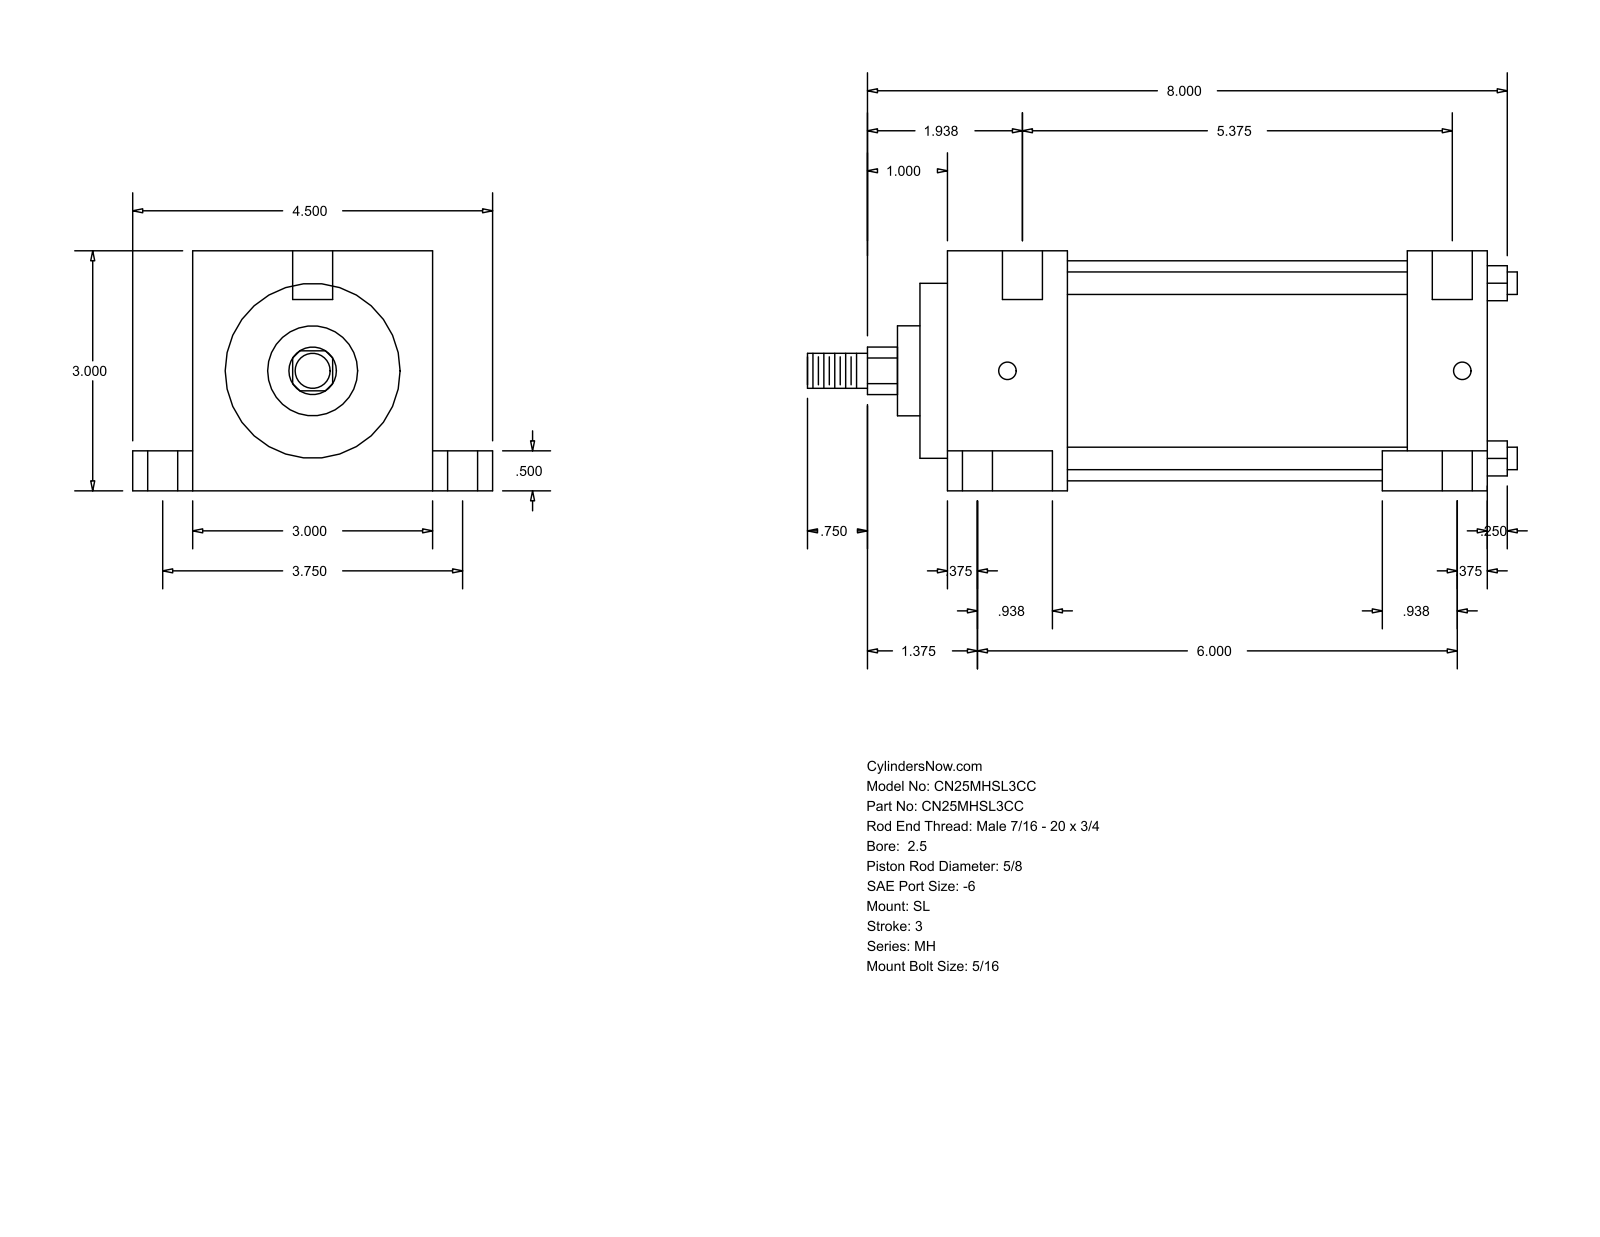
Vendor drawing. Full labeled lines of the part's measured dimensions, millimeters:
Part name (STEP PRODUCT): MH_SL__0250_0.625
STEP written by: GSSL Pune (CONFIG_CONTROL_DESIGN)
Units: millimetres
Bodies: 0 solids, 86 faces (61 planar, 25 cylindrical, 0 other)
Overall size (bounding box): 225.43 × 114.3 × 76.2
Round holes (diameter × count): ⌀5.56 ×2, ⌀9.53 ×2, ⌀15.88 ×2, ⌀12.7 ×1
Round bosses / shafts (diameter × count): ⌀7.14 ×4, ⌀69.85 ×1, ⌀55.55 ×1, ⌀28.57 ×1, ⌀15.88 ×1, ⌀11.11 ×1
Partial cylindrical surfaces — rounded edges, fillets, slot ends (radius × count): R7.54 ×1
Main face-to-face distances: 76.2, 25.4, 154.78, 180.18, 63.5, 12.7, 19.05, 95.25, 31.75, 146.84
Hole centre spacings: 47.65, 3.17, 95.24
